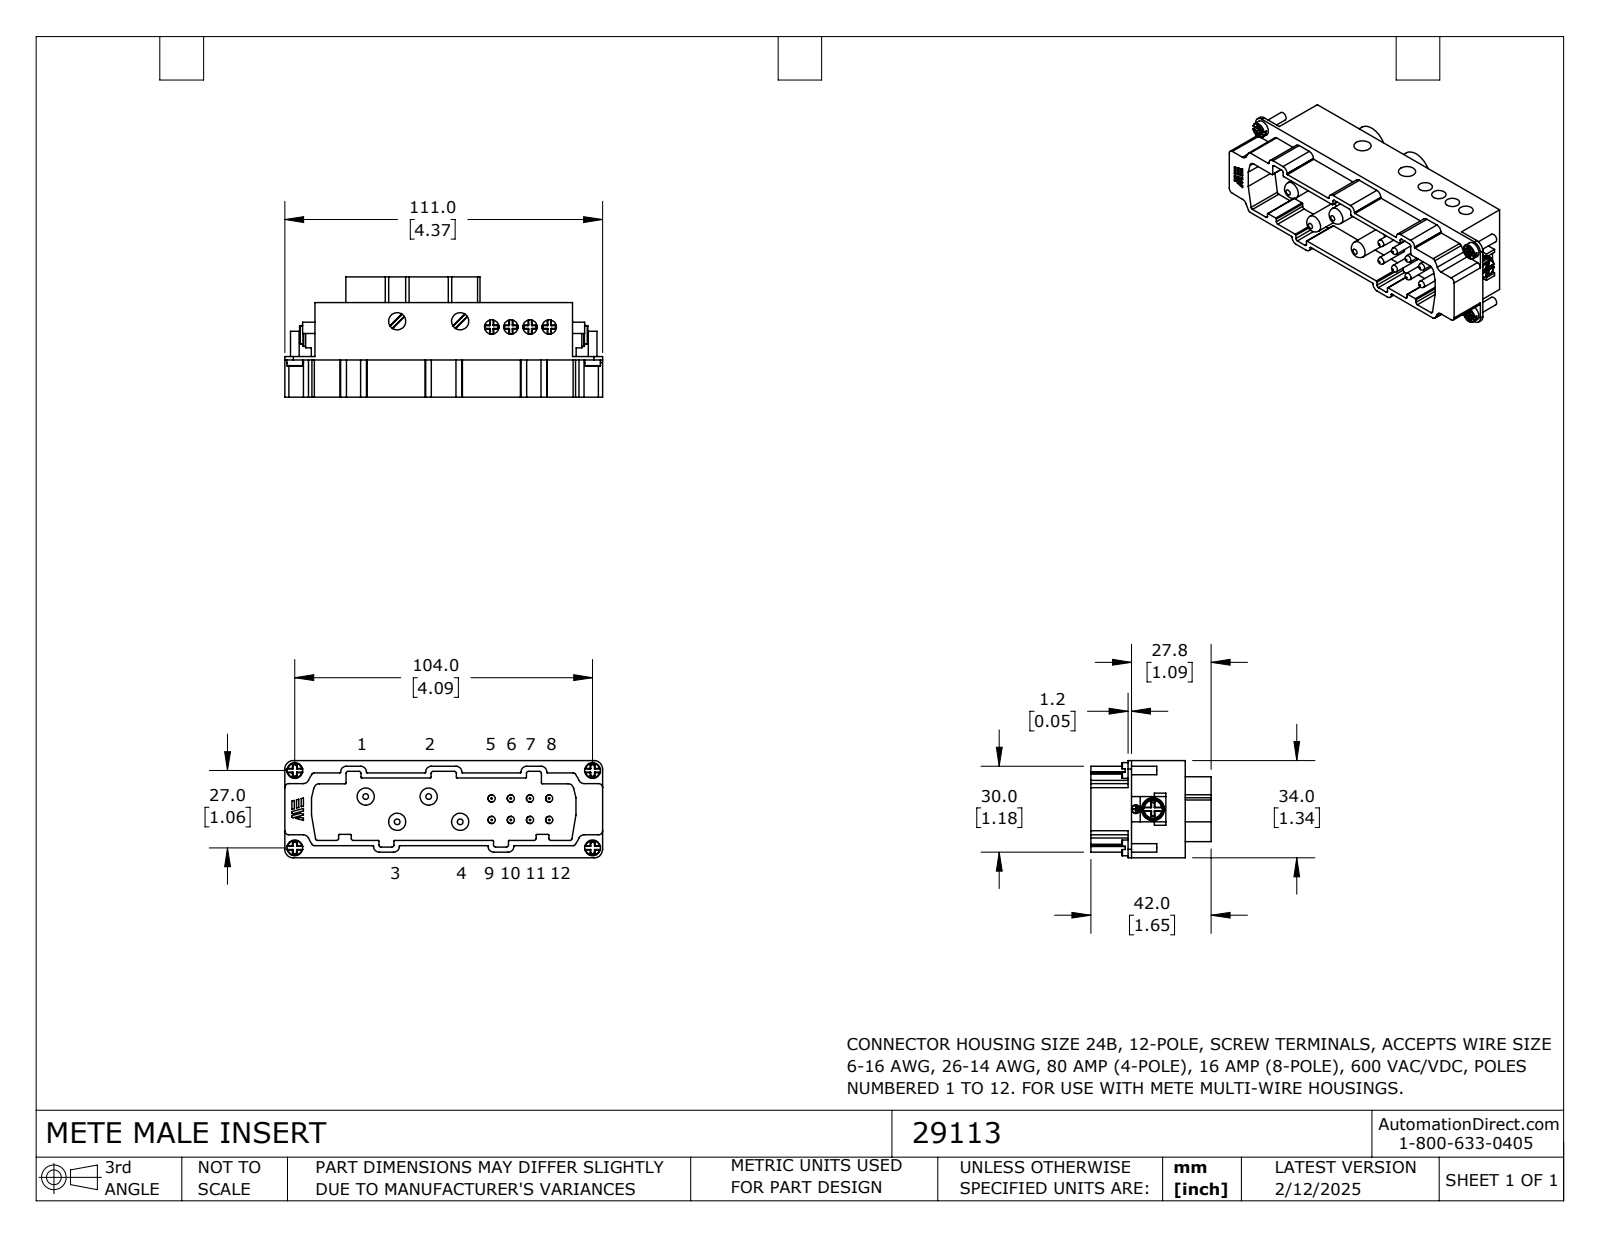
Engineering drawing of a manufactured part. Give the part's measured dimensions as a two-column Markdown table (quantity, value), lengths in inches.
| quantity | value |
| --- | --- |
| part name | 29113 |
| STEP written by | SolidWorks 2024 (CONFIG_CONTROL_DESIGN) |
| units | inches |
| bodies | 1 solid, 1152 faces (513 planar, 403 cylindrical, 236 other) |
| overall size | 4.37 × 1.654 × 1.339 |
| volume | 4.773 in³ |
| surface area | 39.67 in² |
| round holes (diameter × count) | 0.098 × 8, 0.197 × 4, 0.236 × 4, 0.315 × 4, 0.118 × 1 |
| round bosses / shafts (diameter × count) | 0.236 × 4, 0.217 × 4, 0.118 × 4, 0.315 × 1, 0.261 × 1, 0.11 × 1 |
| partial cylindrical surfaces (radius × count) | 0.008 × 94, 0.012 × 16, 0.079 × 16, 0.012 × 10, 0.027 × 10, 0.027 × 6, 0.047 × 6, 0.012 × 4 |
| main face-to-face distances | 0.787, 1.169, 0.241, 0.169, 1.339, 1.098, 0.071, 0.929, 0.512, 0.047 |
| hole center spacings | 0.264, 0.396, 0.528, 0.295, 0.605, 0.866, 0.433, 0.555 |
